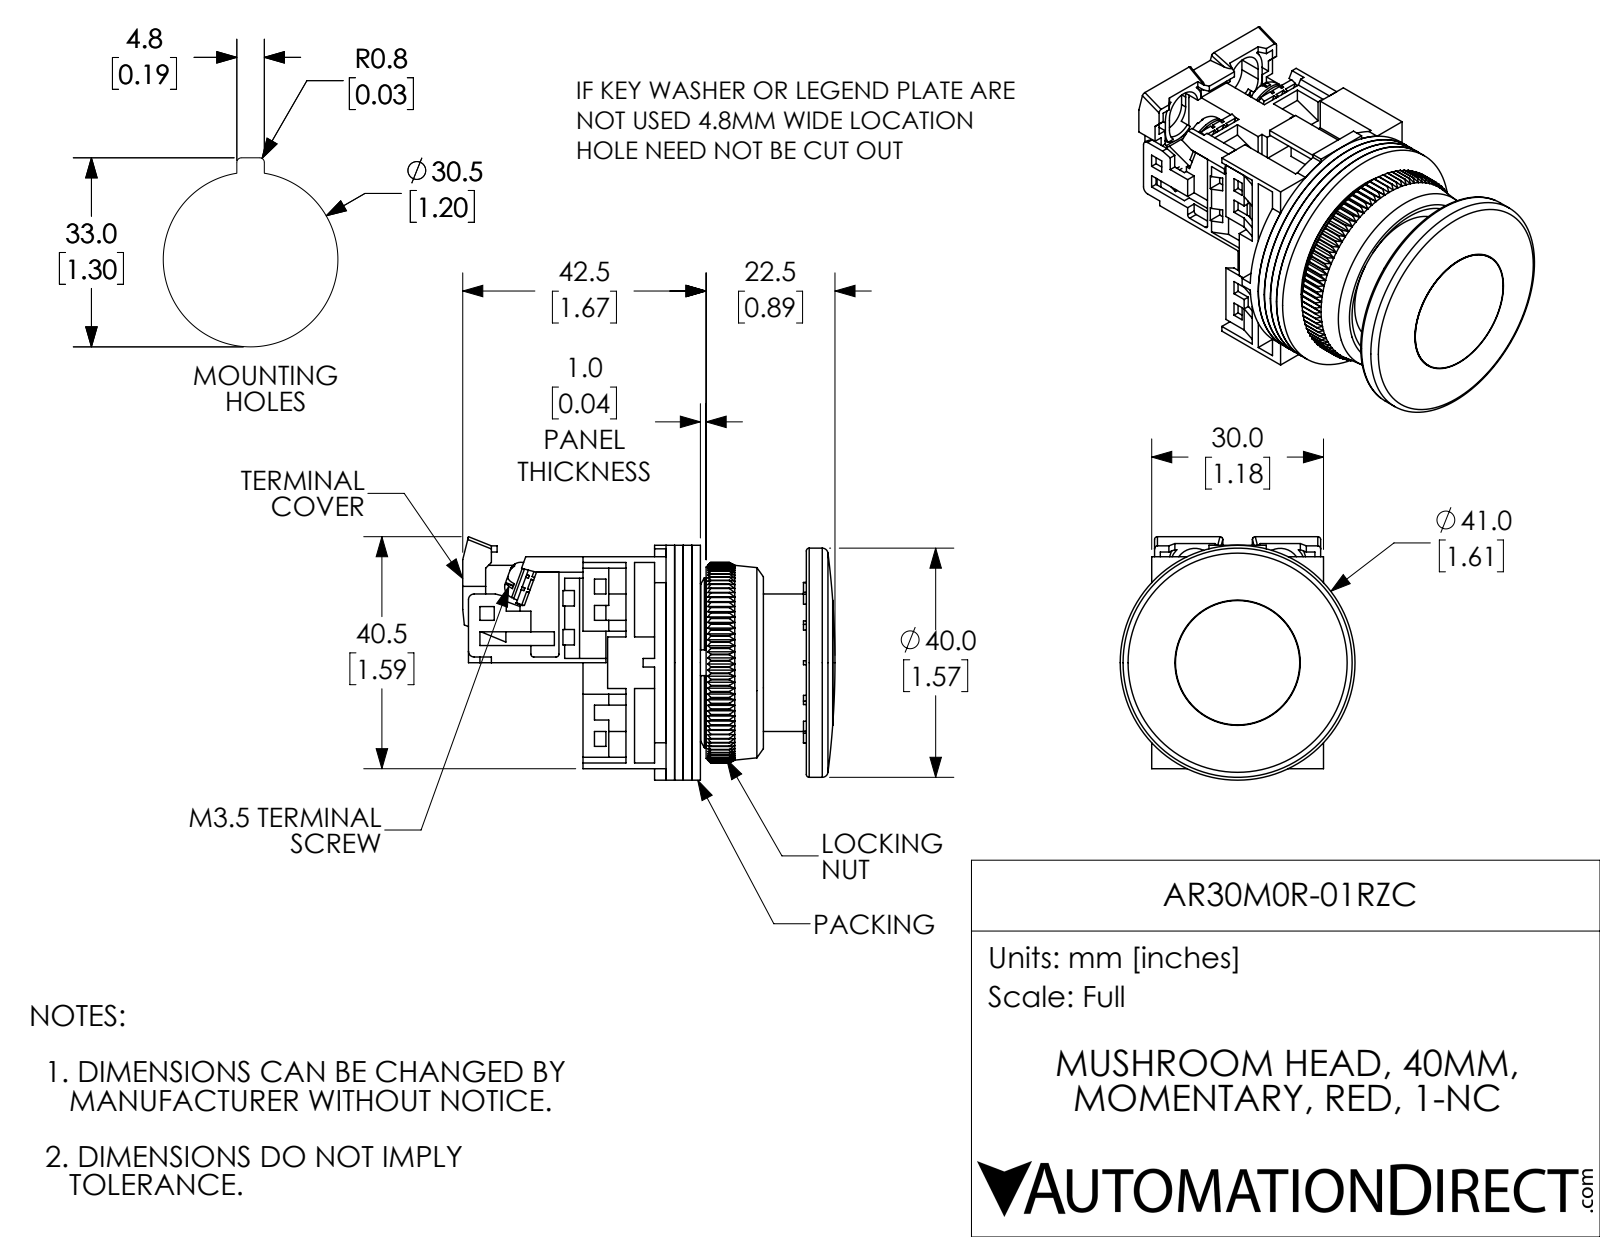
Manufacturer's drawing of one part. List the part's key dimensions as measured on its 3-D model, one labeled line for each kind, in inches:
Part name (STEP PRODUCT): AR30M0R-01RZC
STEP written by: SolidWorks 2017 (AUTOMOTIVE_DESIGN)
Units: inches
Bodies: 15 solids, 1278 faces (819 planar, 260 cylindrical, 199 other)
Overall size (bounding box): 2.559 × 1.673 × 1.614
Volume: 2.225 in³ · Surface area: 48.33 in²
Round holes (diameter × count): ⌀0.138 ×4, ⌀0.142 ×2, ⌀0.118 ×1, ⌀0.709 ×1, ⌀0.945 ×1, ⌀1.122 ×1, ⌀1.252 ×1, ⌀1.417 ×1
Round bosses / shafts (diameter × count): ⌀0.26 ×2, ⌀0.138 ×2, ⌀1.614 ×1, ⌀1.575 ×1, ⌀1.181 ×1, ⌀0.854 ×1
Partial cylindrical surfaces — rounded edges, fillets, slot ends (radius × count): R0.059 ×8, R0.02 ×6, R0.039 ×2, R0.138 ×2, R0.177 ×2, R0.118 ×1, R0.398 ×1, R0.449 ×1
Main face-to-face distances: 0.059, 0.118, 0.177, 0.039, 0.079, 0.689, 0.728, 0.866, 0.807, 1.417
Hole centre spacings: 0.579, 0.61
